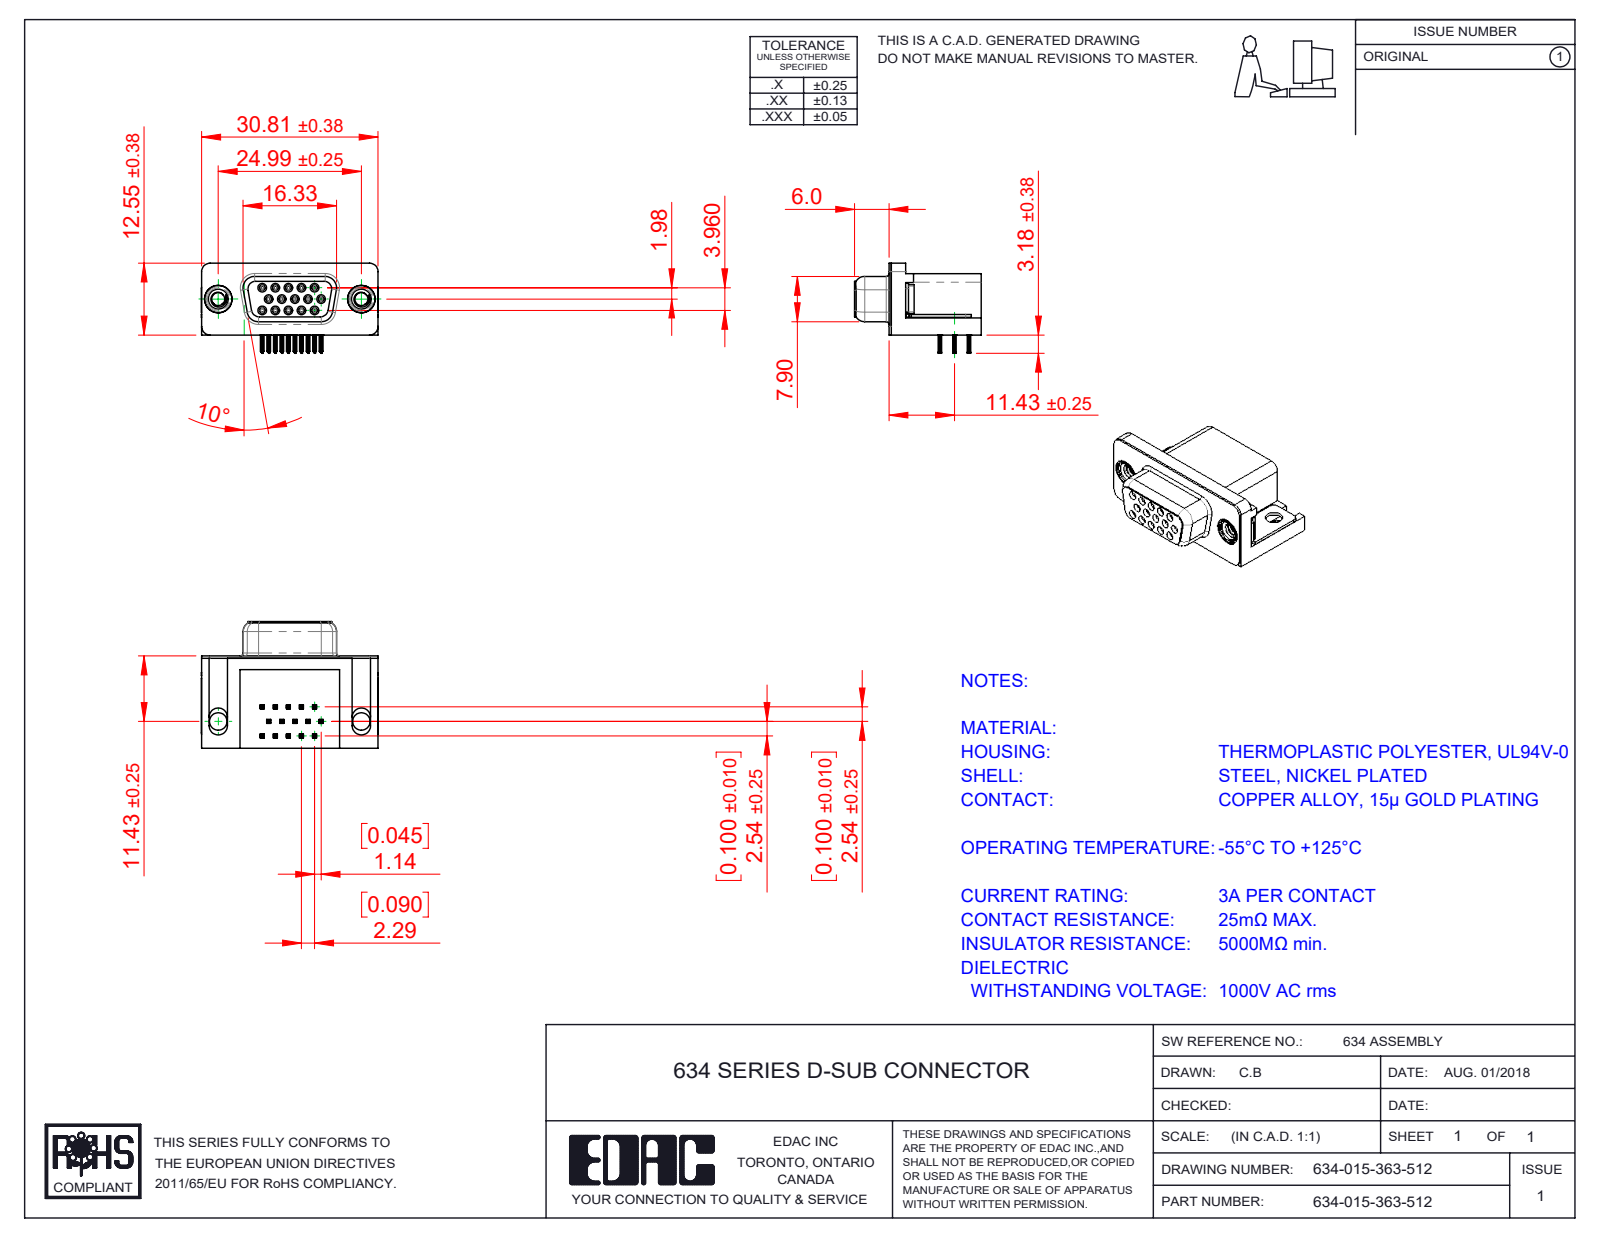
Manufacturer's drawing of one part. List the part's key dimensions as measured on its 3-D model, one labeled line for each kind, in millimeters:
Part name (STEP PRODUCT): Contact Top; 634 Shell; Contact Bottom; 634 Housing (+4 more)
STEP written by: SolidWorks 2016 (CONFIG_CONTROL_DESIGN)
Units: millimetres
Bodies: 21 solids, 2419 faces (1064 planar, 599 cylindrical, 756 other)
Overall size (bounding box): 30.89 × 22.1 × 15.73
Volume: 4 553 mm³ · Surface area: 6 489 mm²
Round holes (diameter × count): ⌀0.8 ×15, ⌀0.9 ×15, ⌀2.26 ×2, ⌀3.05 ×2, ⌀4 ×2, ⌀4.8 ×2, ⌀5 ×2
Round bosses / shafts (diameter × count): ⌀1.2 ×15, ⌀4.9 ×2, ⌀4.75 ×2, ⌀3.9 ×2
Partial cylindrical surfaces — rounded edges, fillets, slot ends (radius × count): R0.1 ×120, R0.15 ×60, R0.35 ×30, R1 ×19, R0.34 ×15, R0.25 ×8, R1.35 ×8, R1.6 ×8
Main face-to-face distances: 0.4, 10.35, 15.7, 16.1, 0.35, 0.6, 2.5, 2.9, 0.5, 6.4
Hole centre spacings: 2.29, 2.28, 3.96, 4.57, 6.05, 3.97, 4.58, 6.86
